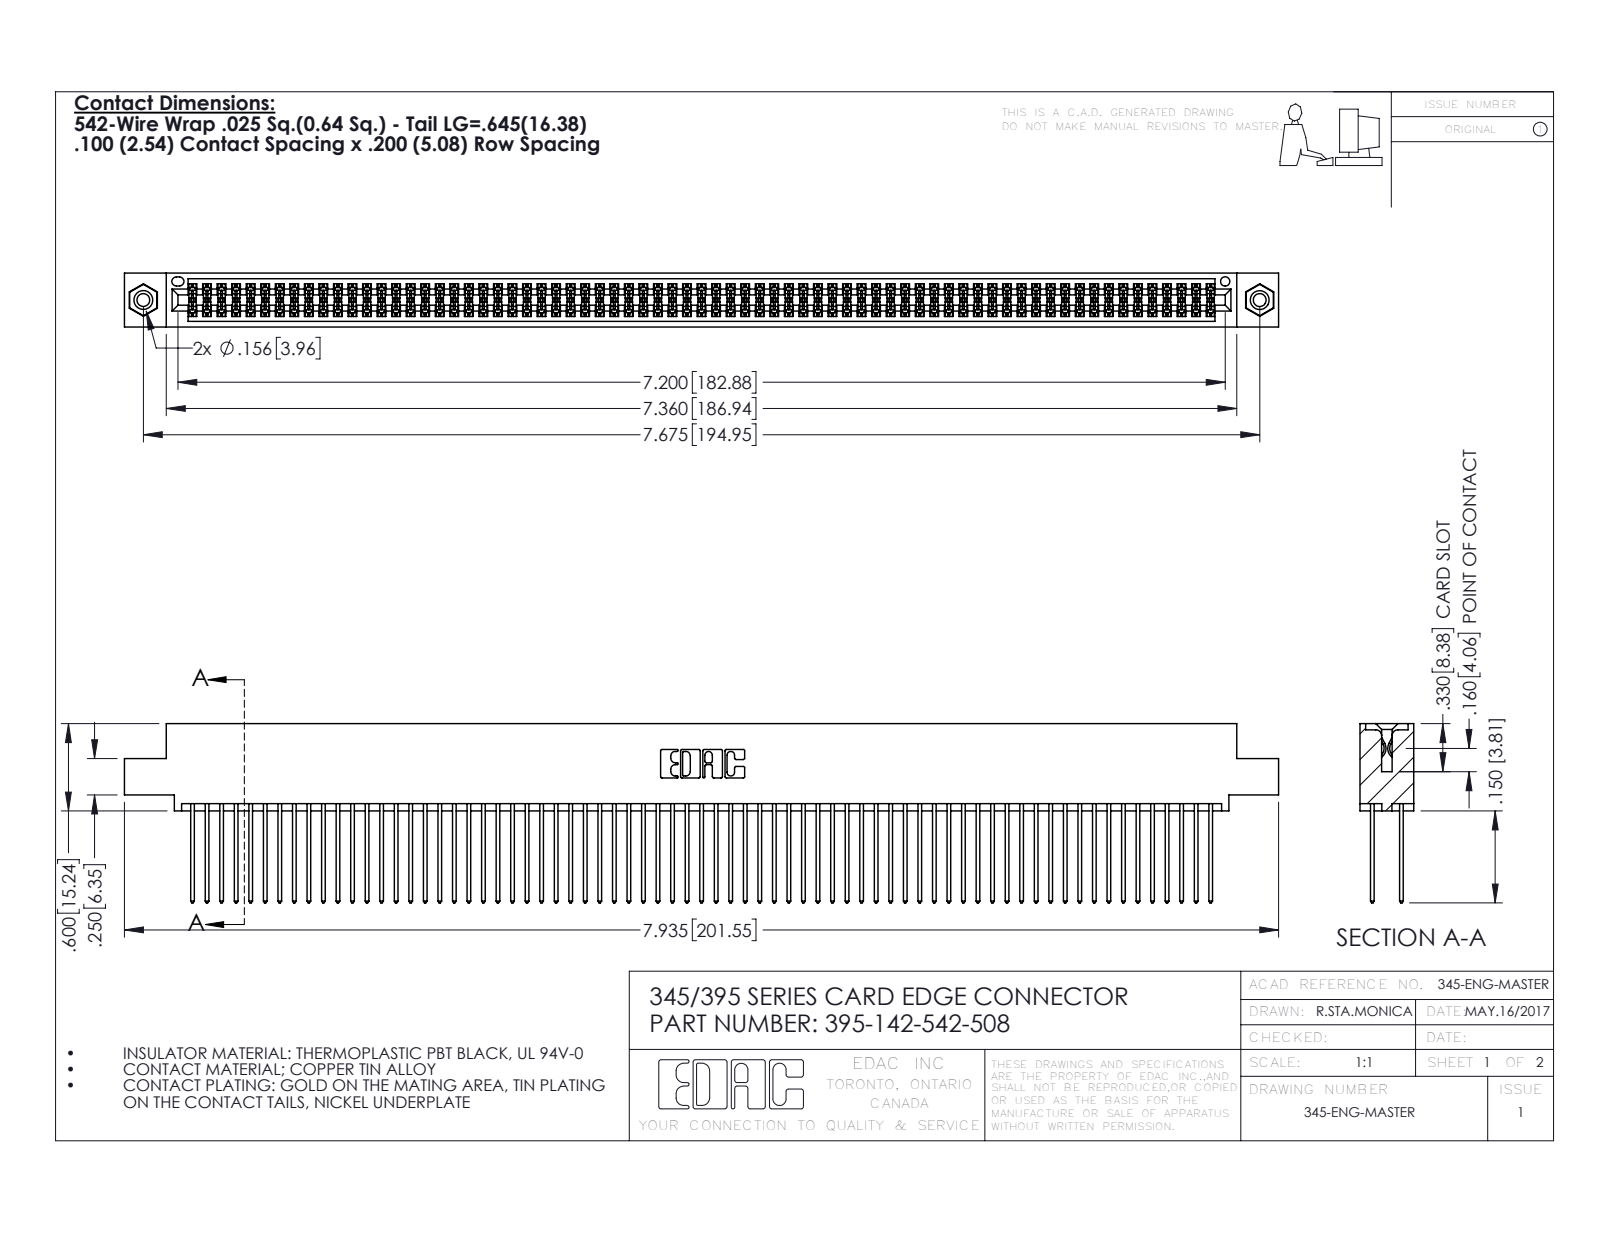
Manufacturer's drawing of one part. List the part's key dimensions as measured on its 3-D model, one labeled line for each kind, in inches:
Part name (STEP PRODUCT): 345-292-001_345-293-142; 395-142-542-508; 345-250-001_345-250-003-102; 345 Part_0.110 Offset - 0.156 Dia-TI
STEP written by: SolidWorks 2016 (CONFIG_CONTROL_DESIGN)
Units: inches
Bodies: 145 solids, 7290 faces (4802 planar, 2472 cylindrical, 16 other)
Overall size (bounding box): 7.935 × 1.232 × 0.37
Volume: 1.247 in³ · Surface area: 52.64 in²
Round holes (diameter × count): ⌀0.089 ×2, ⌀0.125 ×2, ⌀0.156 ×2, ⌀0.064 ×1
Round bosses / shafts (diameter × count): ⌀0.155 ×2
Partial cylindrical surfaces — rounded edges, fillets, slot ends (radius × count): R0.006 ×213, R0.01 ×142, R0.01 ×22, R0.007 ×6, R0.031 ×6, R0.026 ×3, R0.014 ×2, R0.019 ×2
Main face-to-face distances: 0.072, 0.298, 0.2, 0.098, 0.272, 0.025, 0.225, 0.37, 0.175, 0.149
Hole centre spacings: 0.27, 7.439, 7.675
